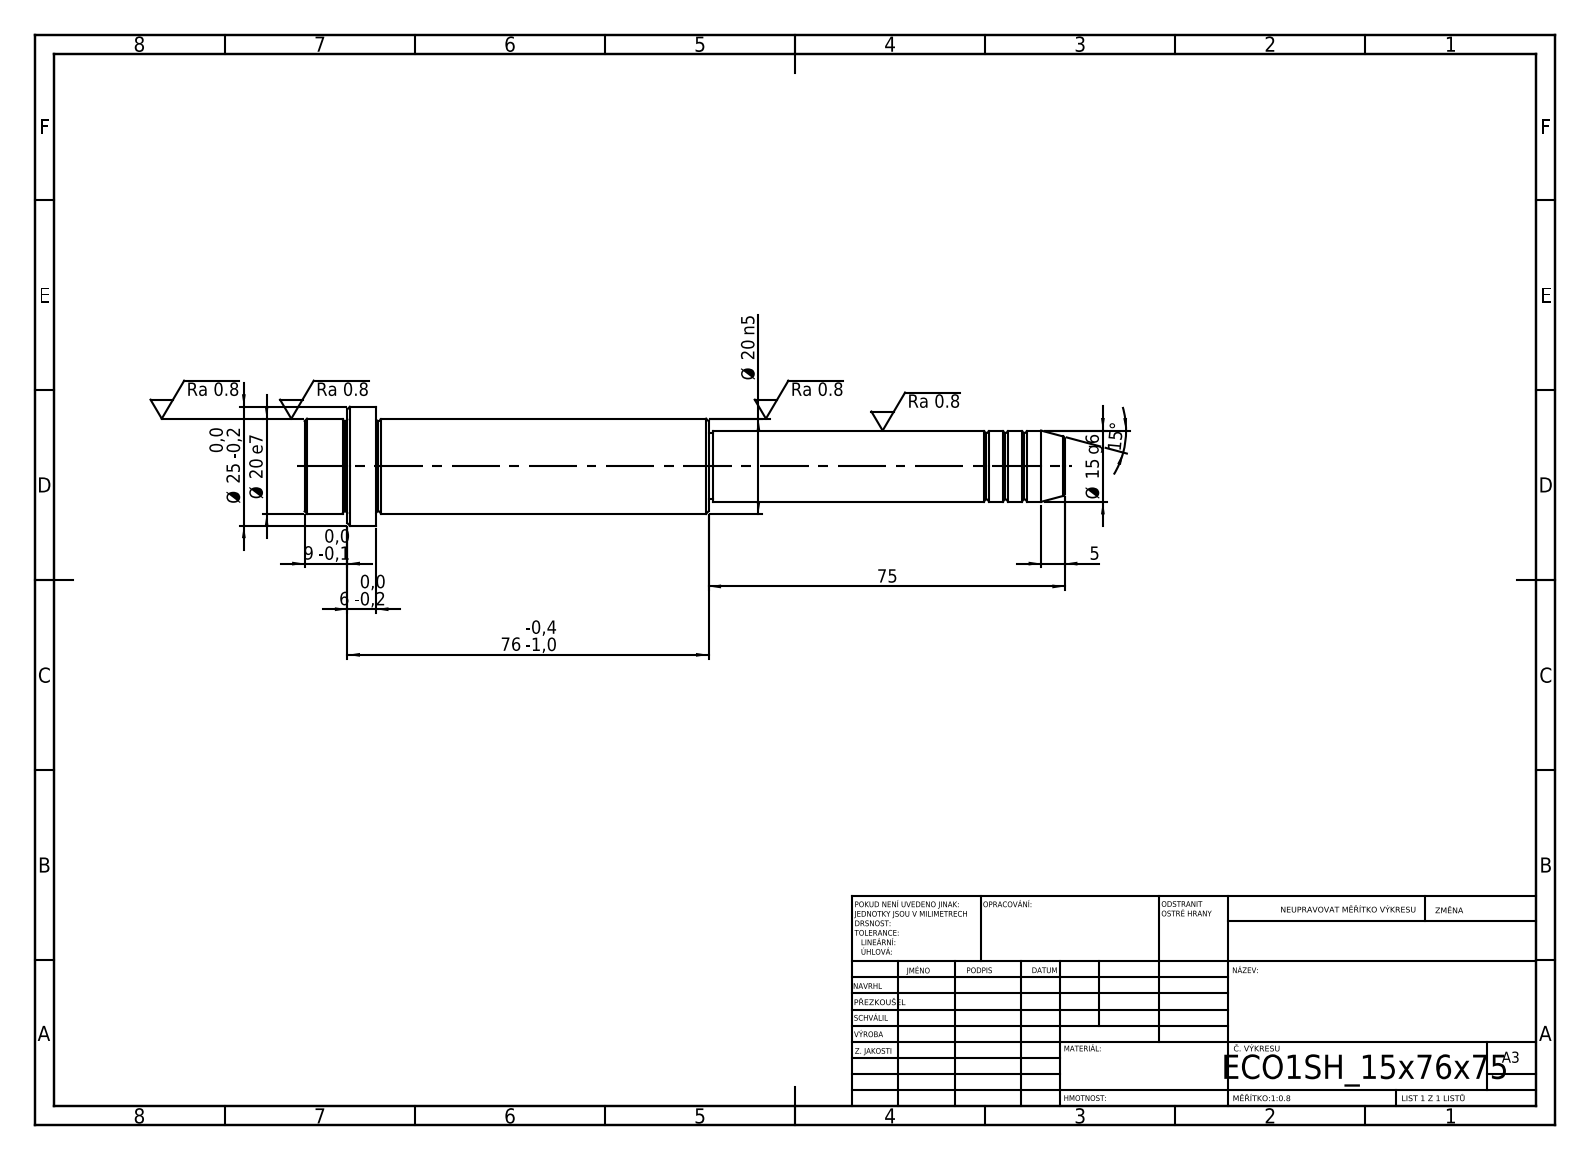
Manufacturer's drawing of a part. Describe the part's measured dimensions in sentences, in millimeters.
Its 3-D file was written by "SolidWorks 2019 (CONFIG_CONTROL_DESIGN)". It is 1 solid with 52 faces: 6 planar, 16 cylindrical and 30 other. Overall it measures 160 by 25 by 25 millimeters. Its volume is 40 718 cubic millimeters and its surface area 9 994 square millimeters. Round bosses or shafts: 1 of diameter 25, 1 of diameter 20, 1 of diameter 15, 1 of diameter 14. The main face-to-face distances are 15, 6, 9, 70, 76, 85, 75, 145, 151, 160.
